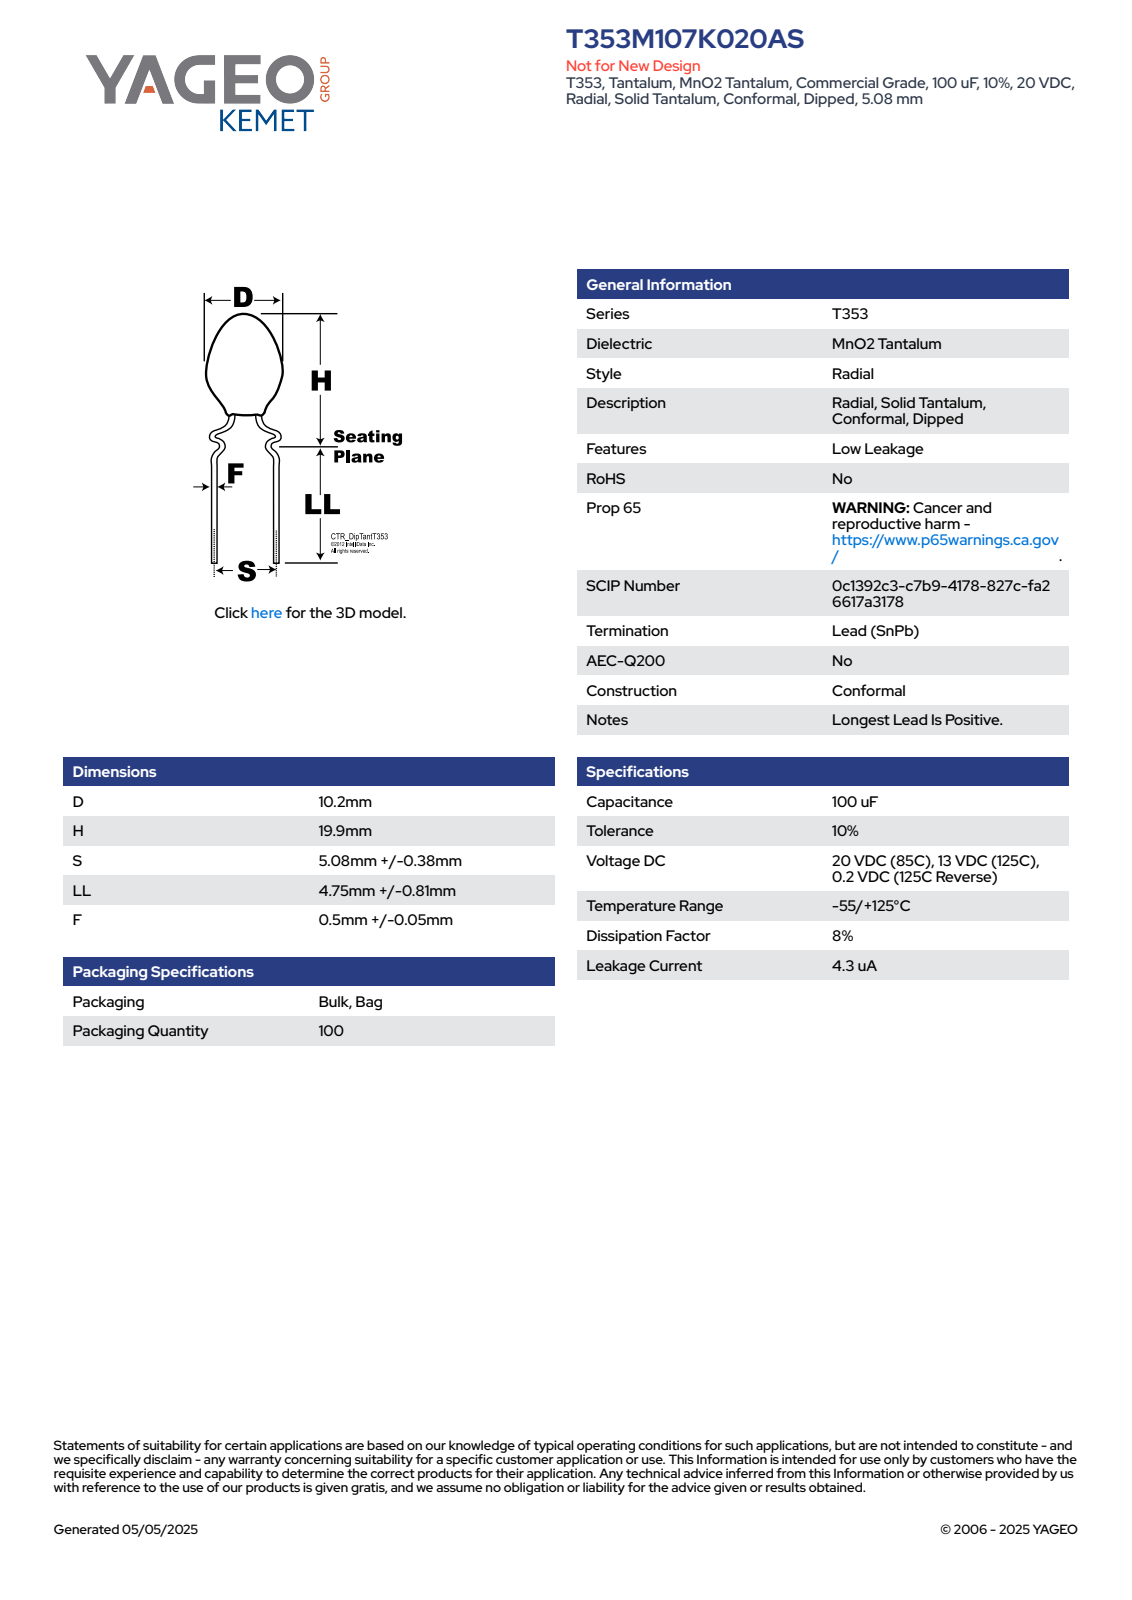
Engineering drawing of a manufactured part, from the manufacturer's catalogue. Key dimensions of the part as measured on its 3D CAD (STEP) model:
Part name (STEP PRODUCT): CTR_T353_D10.2H19.9S5.08LL5.56F0.55
STEP written by: SolidWorks 2014 (AUTOMOTIVE_DESIGN)
Units: millimetres
Bodies: 1 solid, 89 faces (29 planar, 10 cylindrical, 50 other)
Overall size (bounding box): 25.46 × 10.2 × 10.2
Volume: 881 mm³ · Surface area: 501 mm²
Round bosses / shafts (diameter × count): ⌀0.55 ×2, ⌀10.2 ×1
Partial cylindrical surfaces — rounded edges, fillets, slot ends (radius × count): R5.09 ×1
Main face-to-face distances: 13.66, 11.8, 25.46, 19.56, 7.76, 5.9, 17.95, 6.15, 1.61, 7.51
